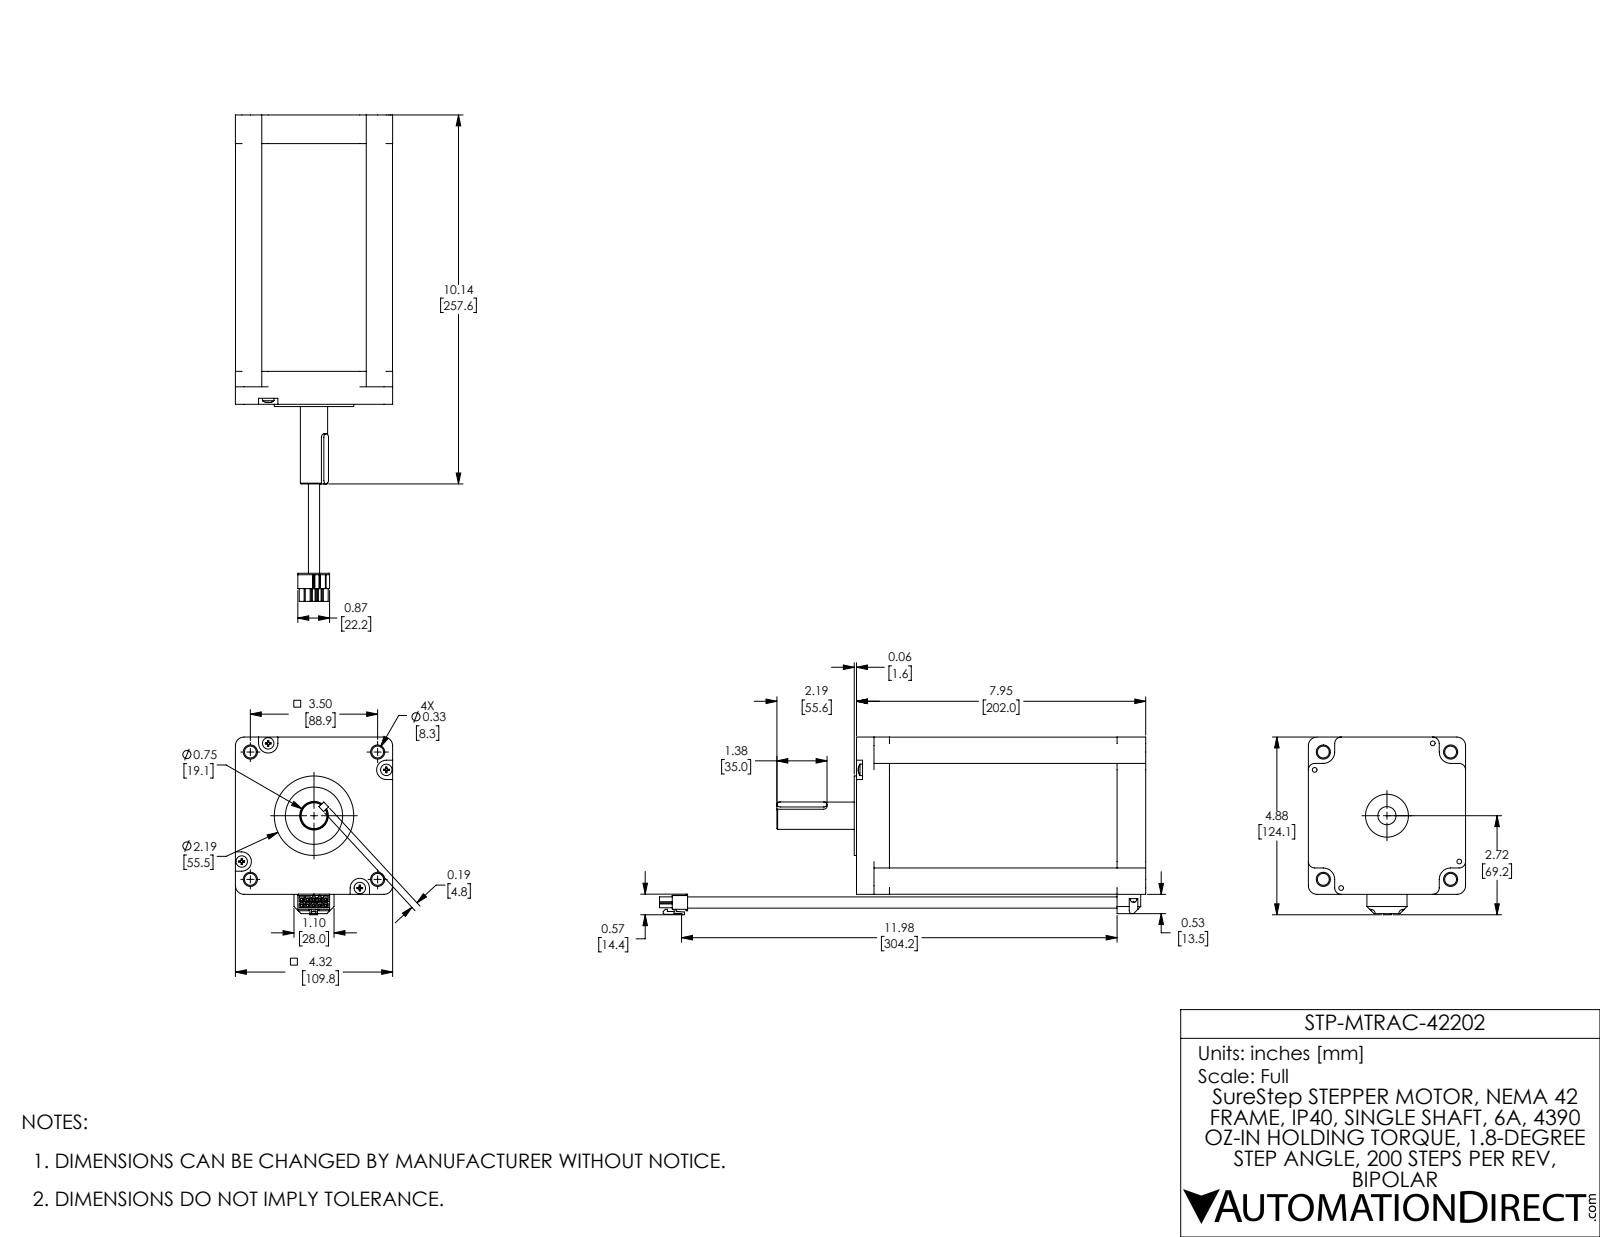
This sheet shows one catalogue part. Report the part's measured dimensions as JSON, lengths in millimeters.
{"part_name": "STP-MTRAC-42202", "step_written_by": "SolidWorks 2017 (AUTOMOTIVE_DESIGN)", "units": "millimeters", "bodies": {"solids": 13, "faces": 997, "planar": 602, "cylindrical": 205, "other": 190}, "overall_size": [339.6, 124.1, 109.8], "volume_mm3": 1038000, "surface_area_mm2": 267300, "round_holes": [[4.5, 8], [3.3, 6], [4.6, 4], [8.3, 4], [15, 1], [20, 1], [28.3, 1], [30, 1], [35, 1], [40, 1], [41.3, 1], [52, 1]], "round_bosses_or_shafts": [[8, 4], [4, 4], [4.5, 2], [65.5, 1], [65, 1], [55.5, 1], [30.7, 1], [25.4, 1]], "partial_cylinders_radius": [[0.3, 22], [4.5, 16], [0.3, 6], [6, 4], [6.8, 4], [8, 4], [2.4, 2], [3, 2]], "face_to_face_distances": [109.7, 109.8, 17, 18.4, 91.4, 18.3, 91.3, 202, 174.5, 20], "hole_center_spacings": [13.8, 59.8, 76.7, 84.6, 95.8, 121.9, 26.2, 62.9]}
